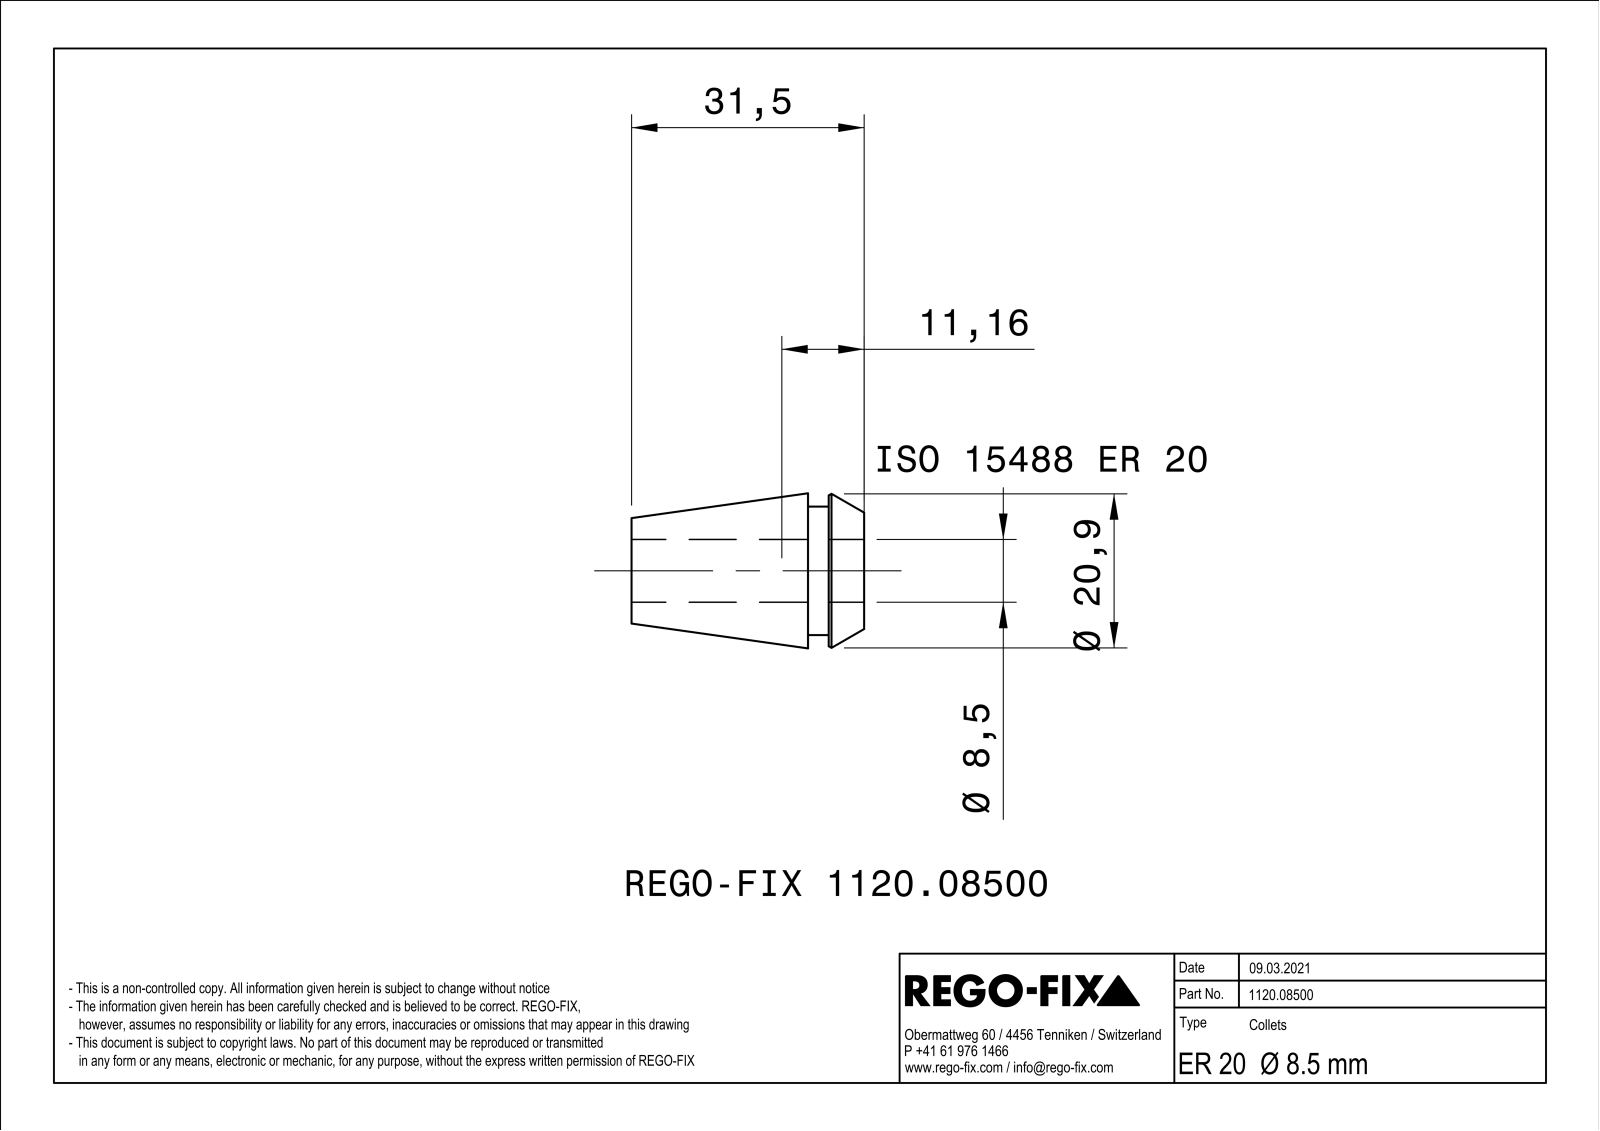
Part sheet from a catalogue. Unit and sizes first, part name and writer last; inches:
Units: inches
Overall size (bounding box): 1.24 × 0.826 × 0.826
Round holes (diameter × count): ⌀0.335 ×1
Round bosses / shafts (diameter × count): ⌀0.685 ×1
Main face-to-face distances: 0.024, 0.299, 1.24, 0.941, 0.189, 0.11, 1.051, 0.217, 0.028, 0.083
Volume: 0.296 in³ · Surface area: 10.28 in²
Bodies: 1 solid, 177 faces (88 planar, 9 cylindrical, 80 other)
Part name (STEP PRODUCT): NOCUT
STEP written by: SIEMENS PLM Software Solid Edge ST10 (AUTOMOTIVE_DESIGN)
